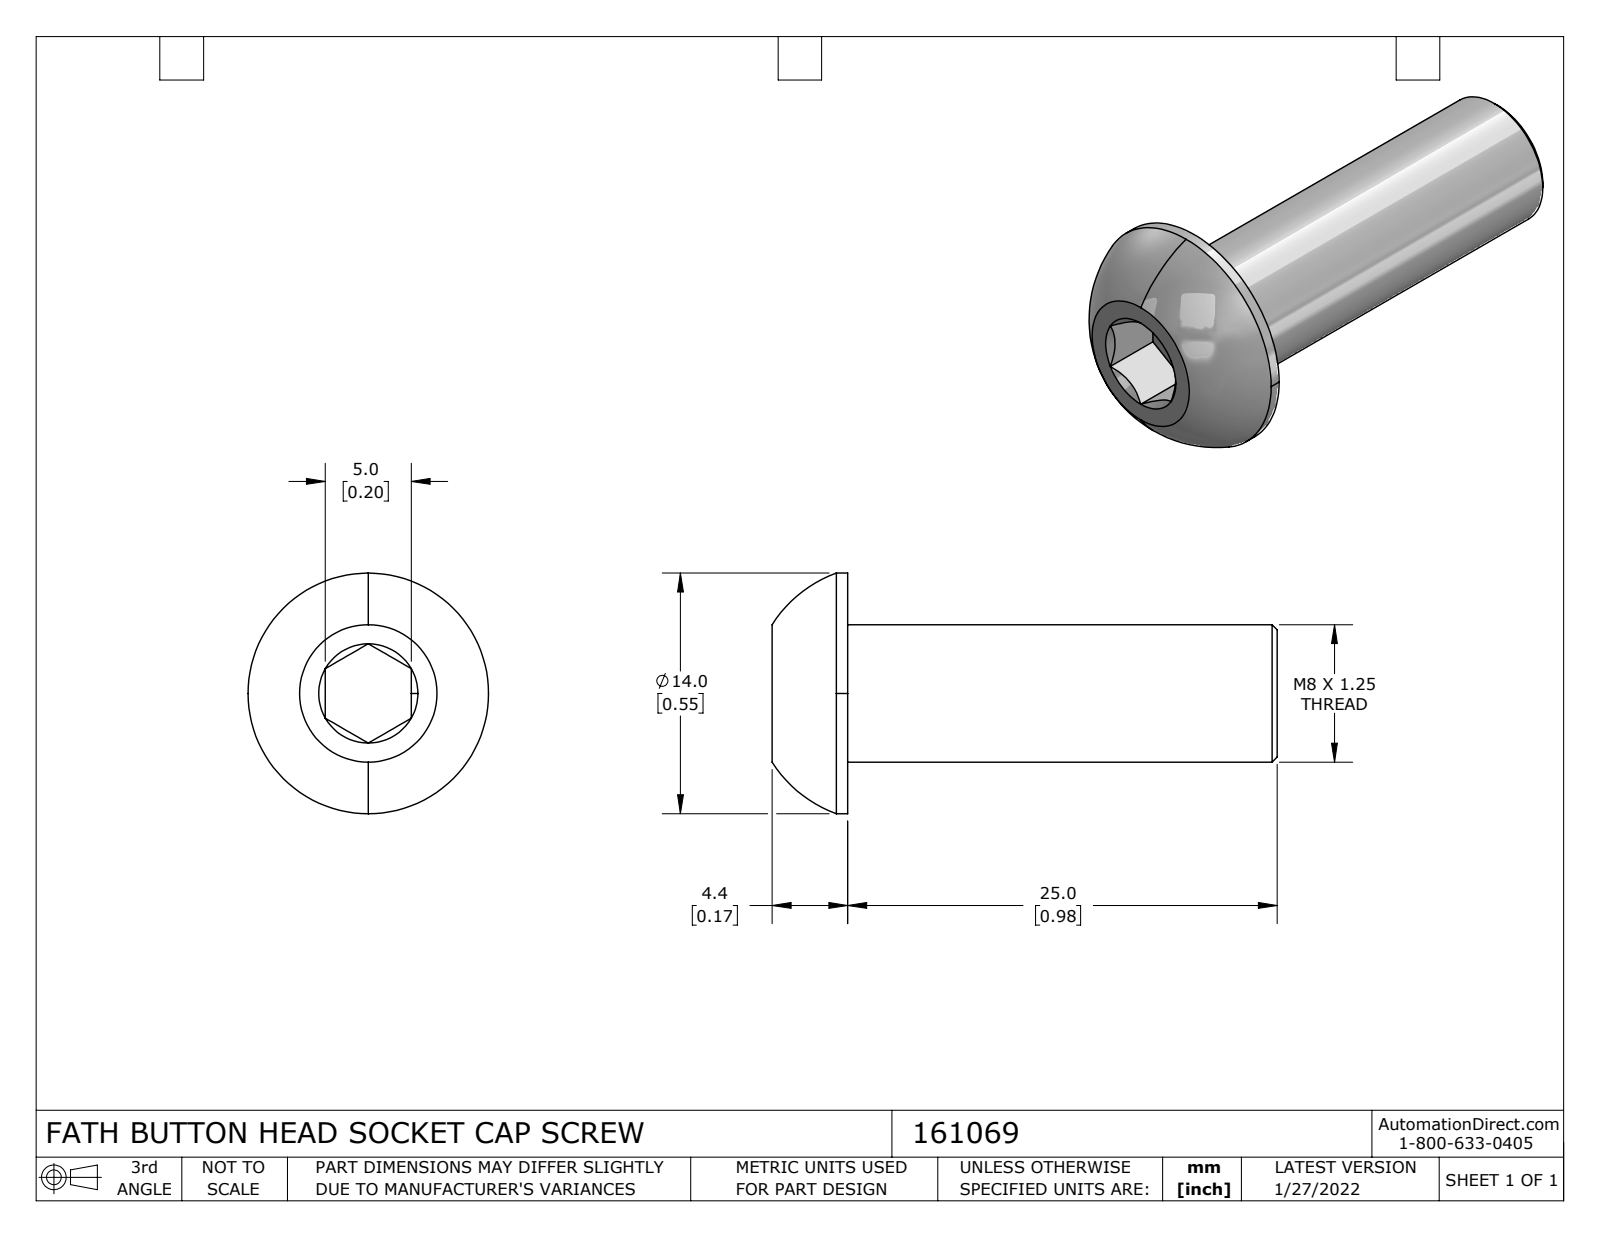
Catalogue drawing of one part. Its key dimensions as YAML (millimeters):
part_name: "161069"
step_written_by: "SolidWorks 2021 (CONFIG_CONTROL_DESIGN)"
units: millimeters
bodies: {solids: 1, faces: 25, planar: 10, cylindrical: 4, other: 11}
overall_size: [29.4, 14, 14]
volume: 1690
surface_area: 1090
round_bosses_or_shafts:
  - {diameter: 14, count: 1}
  - {diameter: 8, count: 1}
face_to_face_distances: [25, 5, 29.4, 4.4, 25.9, 0.9, 3.5]
